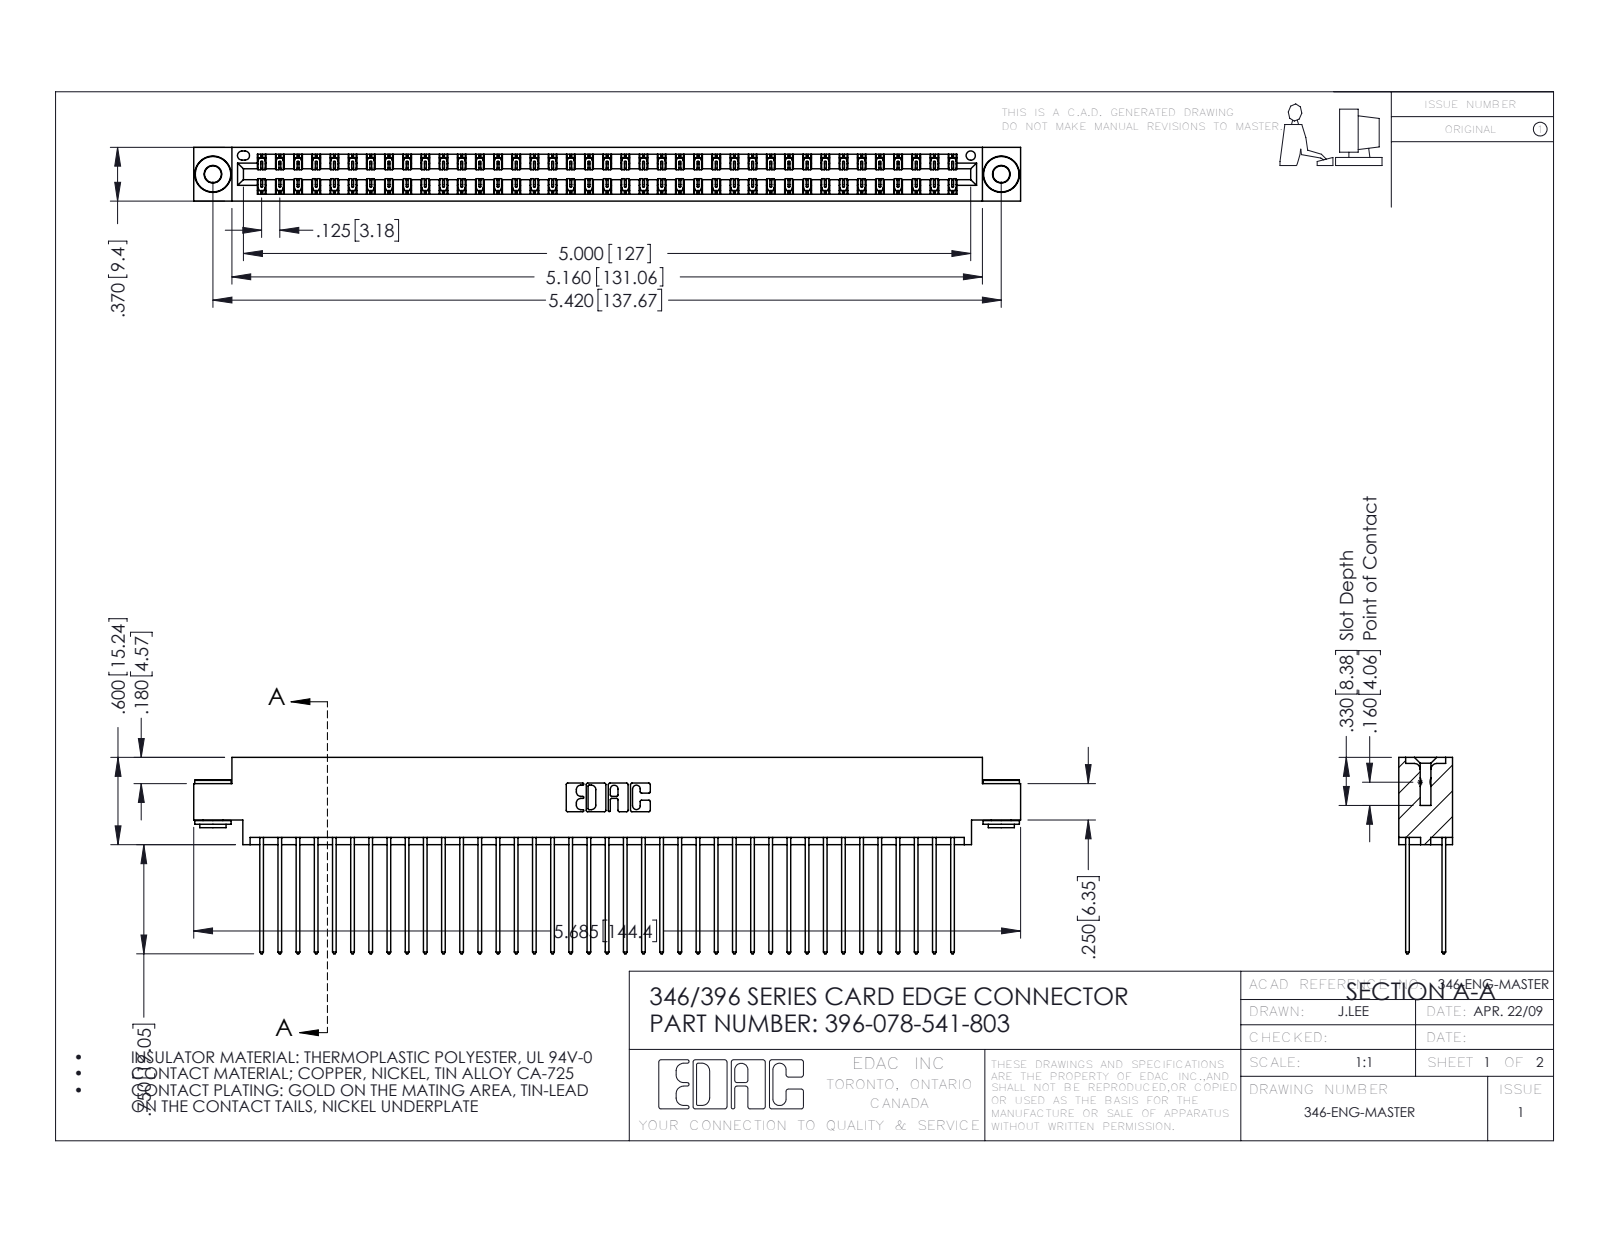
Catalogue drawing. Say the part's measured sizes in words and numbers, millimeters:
The part is named "396-078-541-803; 346 Part_0.170 Offset - 0.156 Dia-TH; 345-292-001_345-293-141; 345-250-002_345-250-002-102". Its 3-D file was written by "SolidWorks 2016 (CONFIG_CONTROL_DESIGN)". It is 81 solids with 4220 faces: 2820 planar, 1392 cylindrical and 8 other. Overall it measures 144.4 by 34.3 by 9.4 millimeters. Its volume is 14 400 cubic millimeters and its surface area 22 250 square millimeters. Round holes: 2 of diameter 2.9, 2 of diameter 4, 1 of diameter 1.6. Round bosses or shafts: 2 of diameter 6.4, 2 of diameter 4.6, 2 of diameter 3.5. Partial cylindrical surfaces (rounded edges, fillets, slot ends): 117 of radius 0.2, 78 of radius 0.3, 22 of radius 0.3, 6 of radius 0.2, 6 of radius 0.8, 3 of radius 0.7, 2 of radius 0.4, 2 of radius 0.6. The main face-to-face distances are 1.2, 8.2, 6.4, 0.6, 1.8, 7.6, 9.4, 7, 5.7, 3.8. The hole center spacings are 6.2, 132.4, 137.7.
